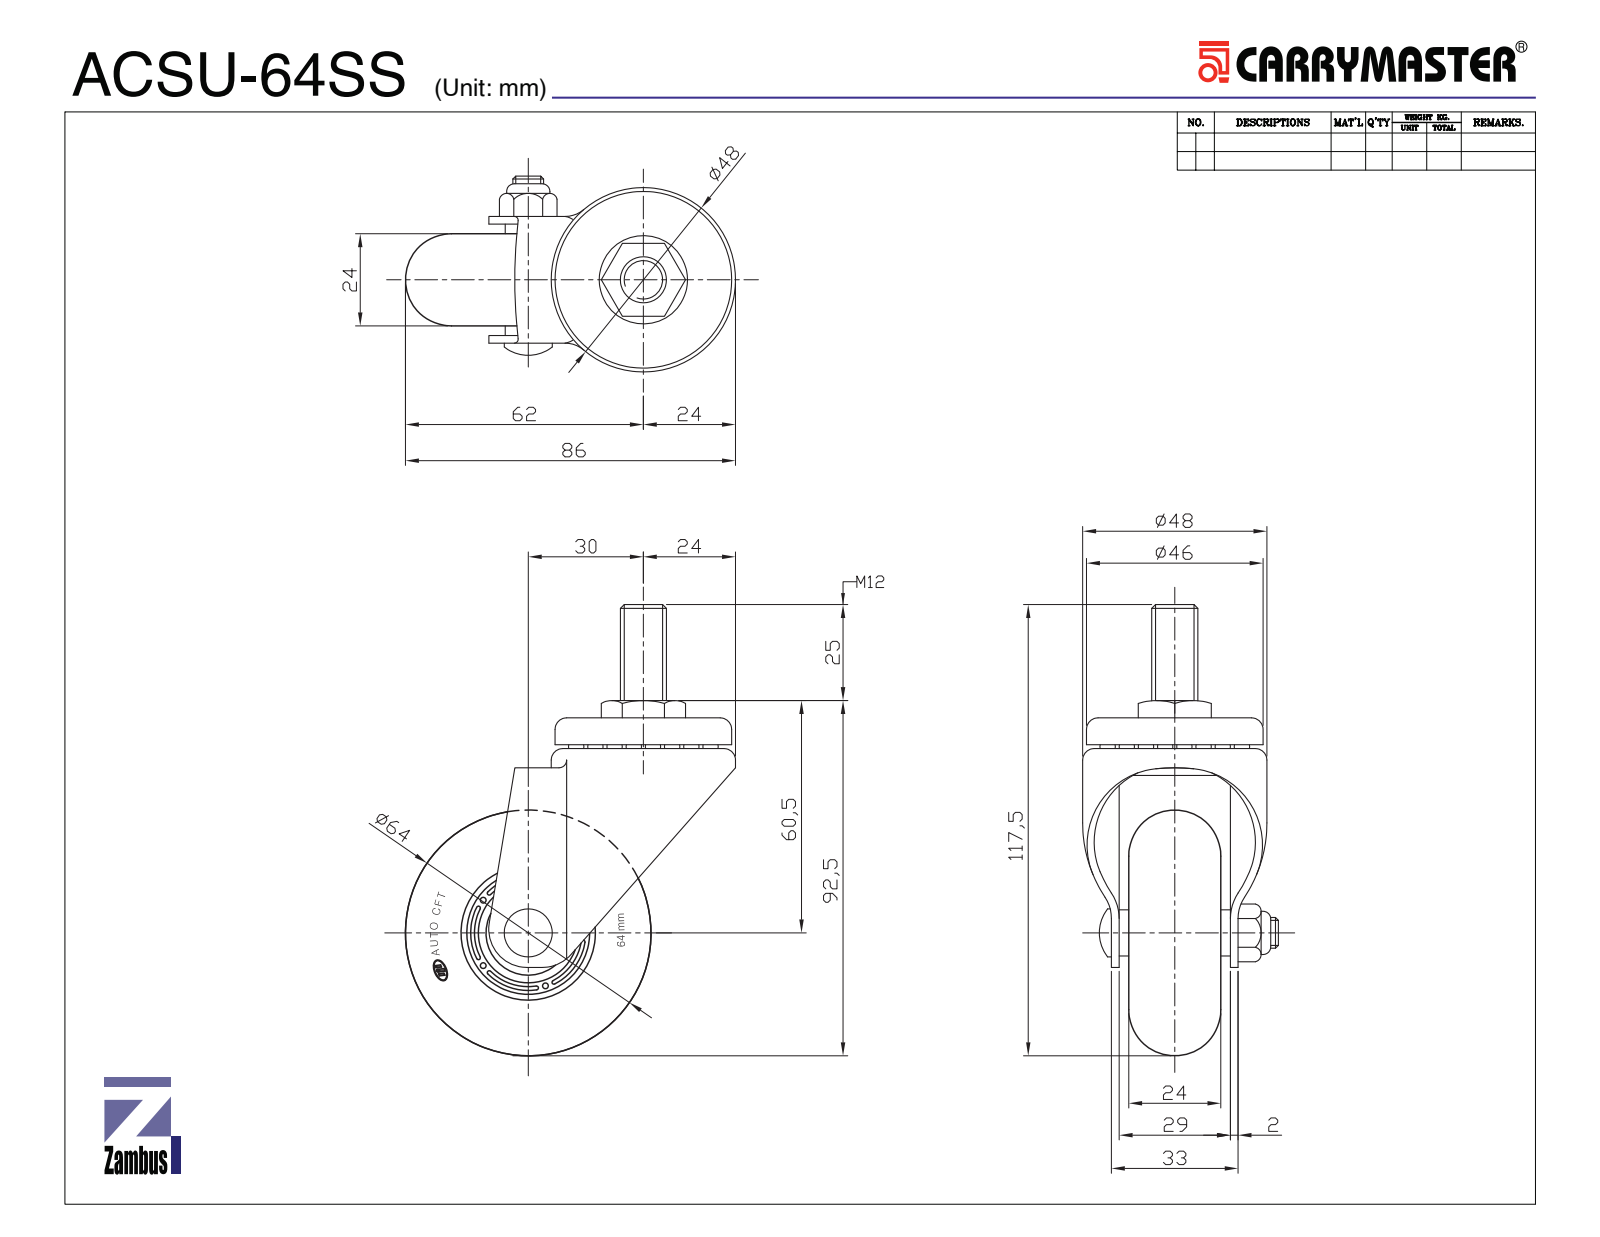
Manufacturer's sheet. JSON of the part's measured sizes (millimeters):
{"part_name": "ACSU-64SS", "step_written_by": "SolidWorks 2015 (CONFIG_CONTROL_DESIGN)", "units": "millimeters", "bodies": {"solids": 15, "faces": 559, "planar": 156, "cylindrical": 231, "other": 172}, "overall_size": [118.41, 84.75, 49.2], "volume_mm3": 93516, "surface_area_mm2": 59856, "round_holes": [[6.8, 1], [8, 1], [8.1, 1], [11, 1], [12.67, 1], [17.33, 1], [18.5, 1], [22, 1], [27, 1], [35, 1], [39.2, 1], [43.5, 1]], "round_bosses_or_shafts": [[47.5, 1], [42.4, 1], [30.3, 1], [18, 1], [16, 1], [12.5, 1], [12, 1], [11.8, 1]], "partial_cylinders_radius": [[1, 60], [1.5, 12], [8, 6], [2, 2], [10, 2], [7, 1], [16, 1], [22, 1]], "face_to_face_distances": [2, 3.5, 35.5, 1.41, 6.75, 30.75, 4.75, 28.75, 1.5, 33.5]}
